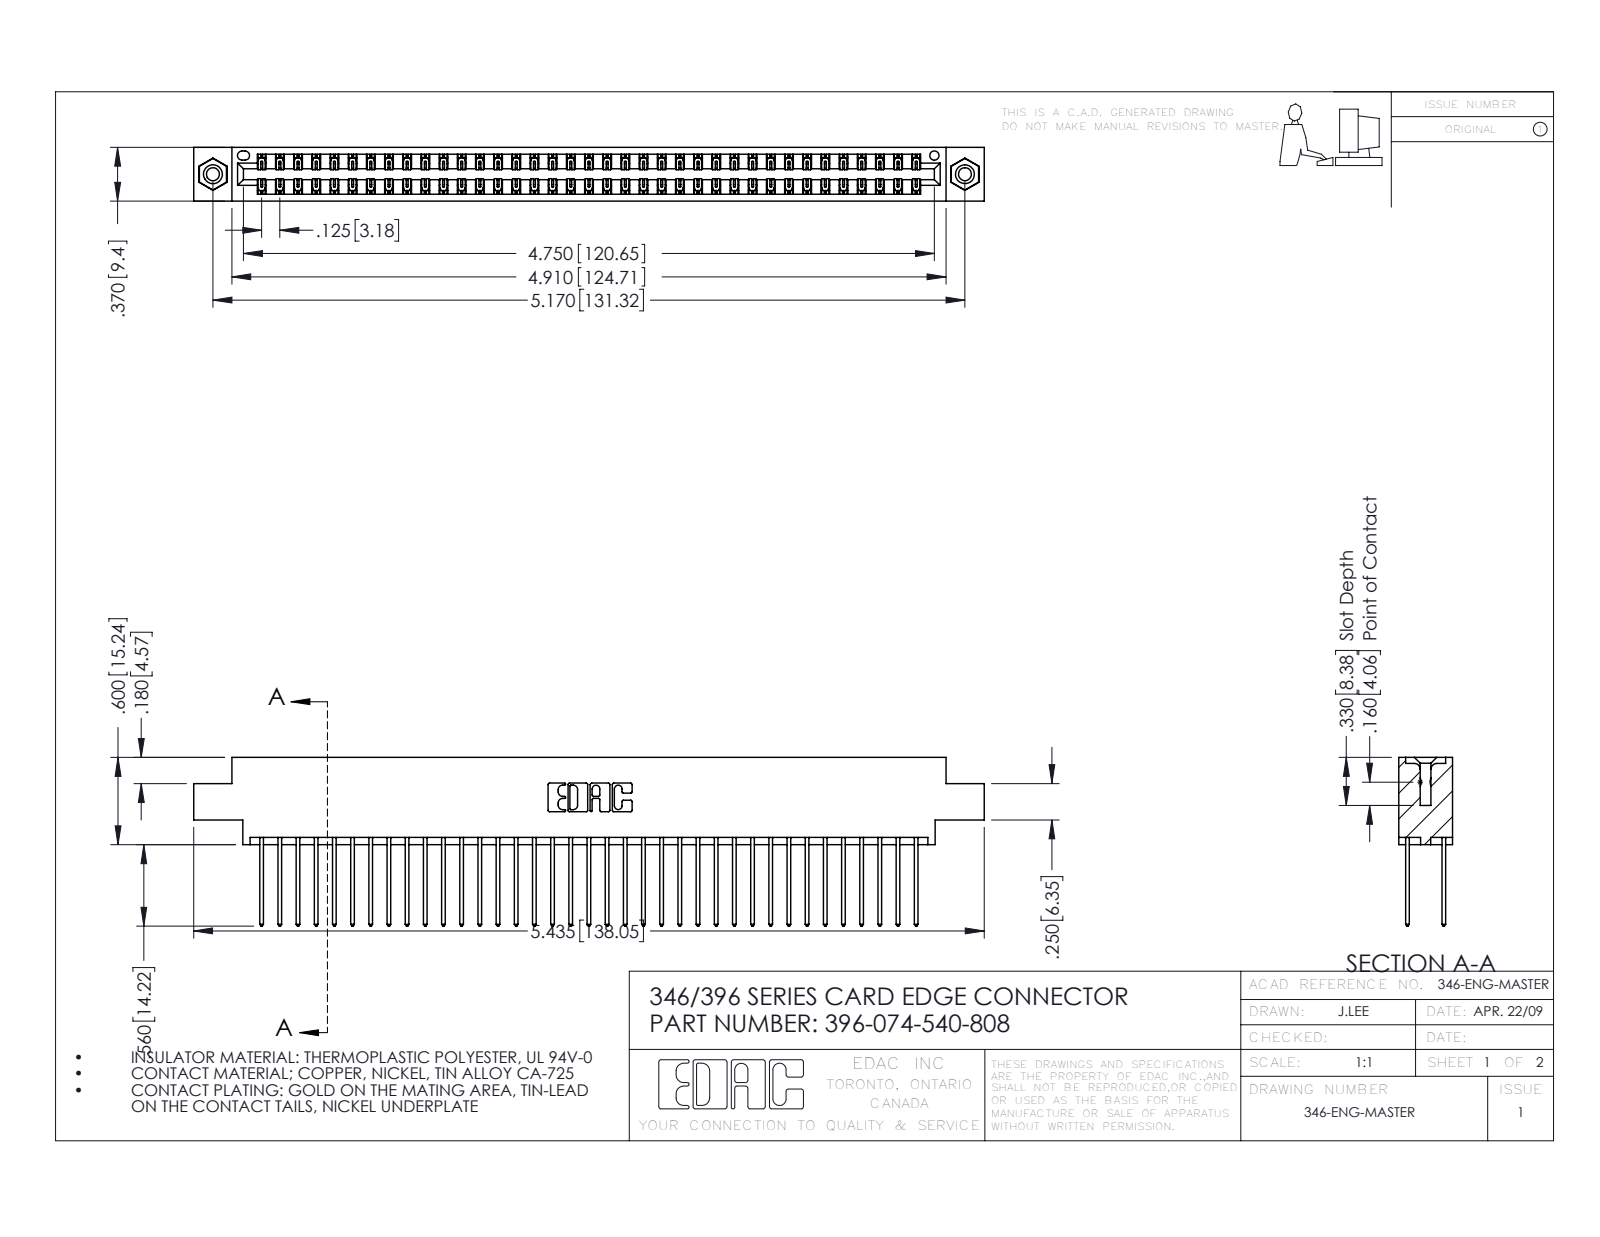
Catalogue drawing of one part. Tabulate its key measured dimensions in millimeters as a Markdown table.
| quantity | value |
| --- | --- |
| part name | 346 Part_0.170 Offset - 0.156 Dia-TI; 345-292-001_345-293-140; 345-250-001_345-250-003-102; 396-074-540-808 |
| STEP written by | SolidWorks 2016 (CONFIG_CONTROL_DESIGN) |
| units | millimeters |
| bodies | 77 solids, 4034 faces (2702 planar, 1316 cylindrical, 16 other) |
| overall size | 138 × 29.5 × 9.4 |
| volume | 13 500 mm³ |
| surface area | 20 060 mm² |
| round holes (diameter × count) | 2.3 × 2, 3.2 × 2, 4 × 2, 1.6 × 1 |
| round bosses / shafts (diameter × count) | 3.9 × 2 |
| partial cylindrical surfaces (radius × count) | 0.2 × 111, 0.3 × 74, 0.3 × 22, 0.2 × 6, 0.8 × 6, 0.7 × 3, 0.4 × 2, 0.6 × 2 |
| main face-to-face distances | 1.2, 8.2, 6.4, 1.8, 7.6, 0.6, 9.4, 7, 5.6, 3.8 |
| hole center spacings | 6.2, 126, 131.3 |
